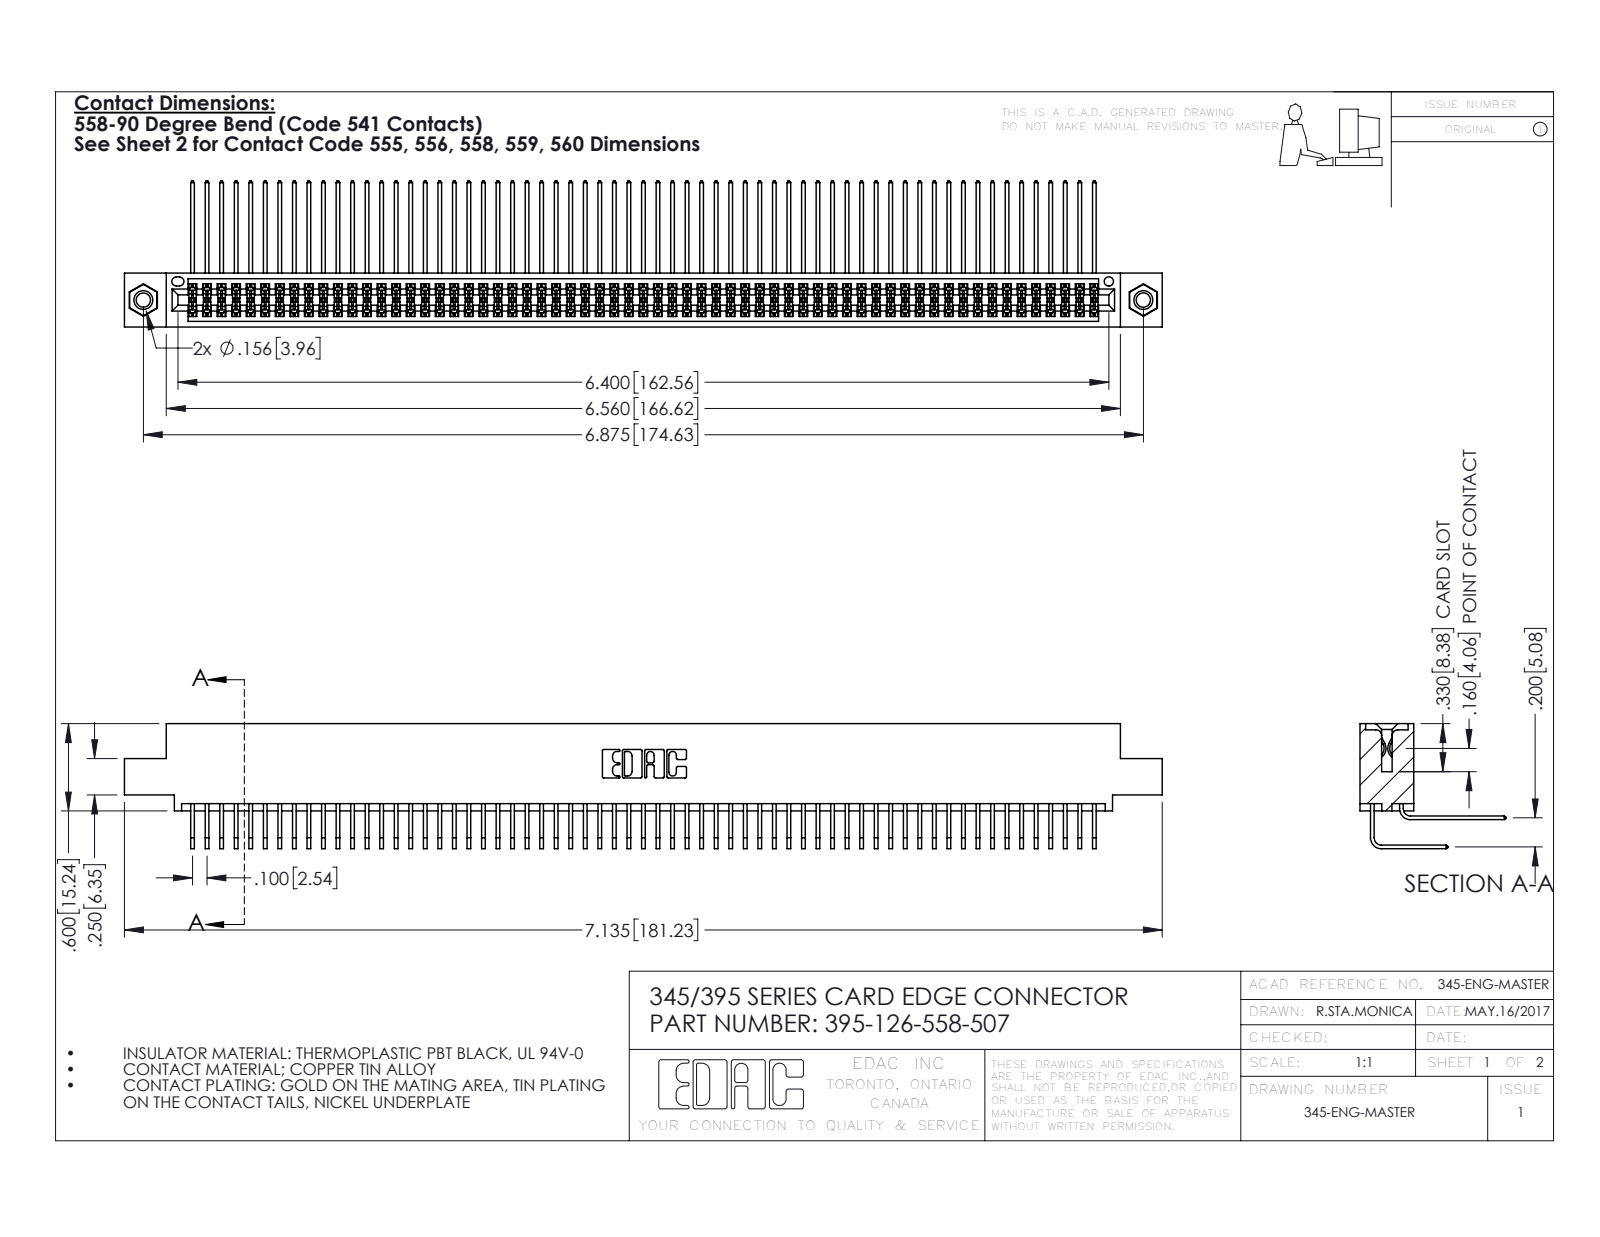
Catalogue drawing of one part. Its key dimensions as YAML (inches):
part_name: "345-292-001_558 Tail - 2; 345-292-001_558 559 Tail - 1; 395-126-558-507; 345-250-001_345-250-005-103 (+1 more)"
step_written_by: "SolidWorks 2016 (CONFIG_CONTROL_DESIGN)"
units: inches
bodies: {solids: 129, faces: 6742, planar: 4526, cylindrical: 2200, other: 16}
overall_size: [7.135, 1.005, 0.859]
volume: 1.125
surface_area: 48.36
round_holes:
  - {diameter: 0.098, count: 2}
  - {diameter: 0.125, count: 2}
  - {diameter: 0.156, count: 2}
  - {diameter: 0.064, count: 1}
round_bosses_or_shafts:
  - {diameter: 0.155, count: 2}
partial_cylinders:
  - {radius: 0.006, count: 190}
  - {radius: 0.01, count: 22}
  - {radius: 0.007, count: 6}
  - {radius: 0.031, count: 6}
  - {radius: 0.026, count: 3}
  - {radius: 0.014, count: 2}
  - {radius: 0.019, count: 2}
  - {radius: 0.022, count: 2}
face_to_face_distances: [0.072, 0.298, 0.2, 0.37, 0.098, 0.272, 0.025, 0.225, 0.025, 0.175]
hole_center_spacings: [0.27, 6.639, 6.875]
